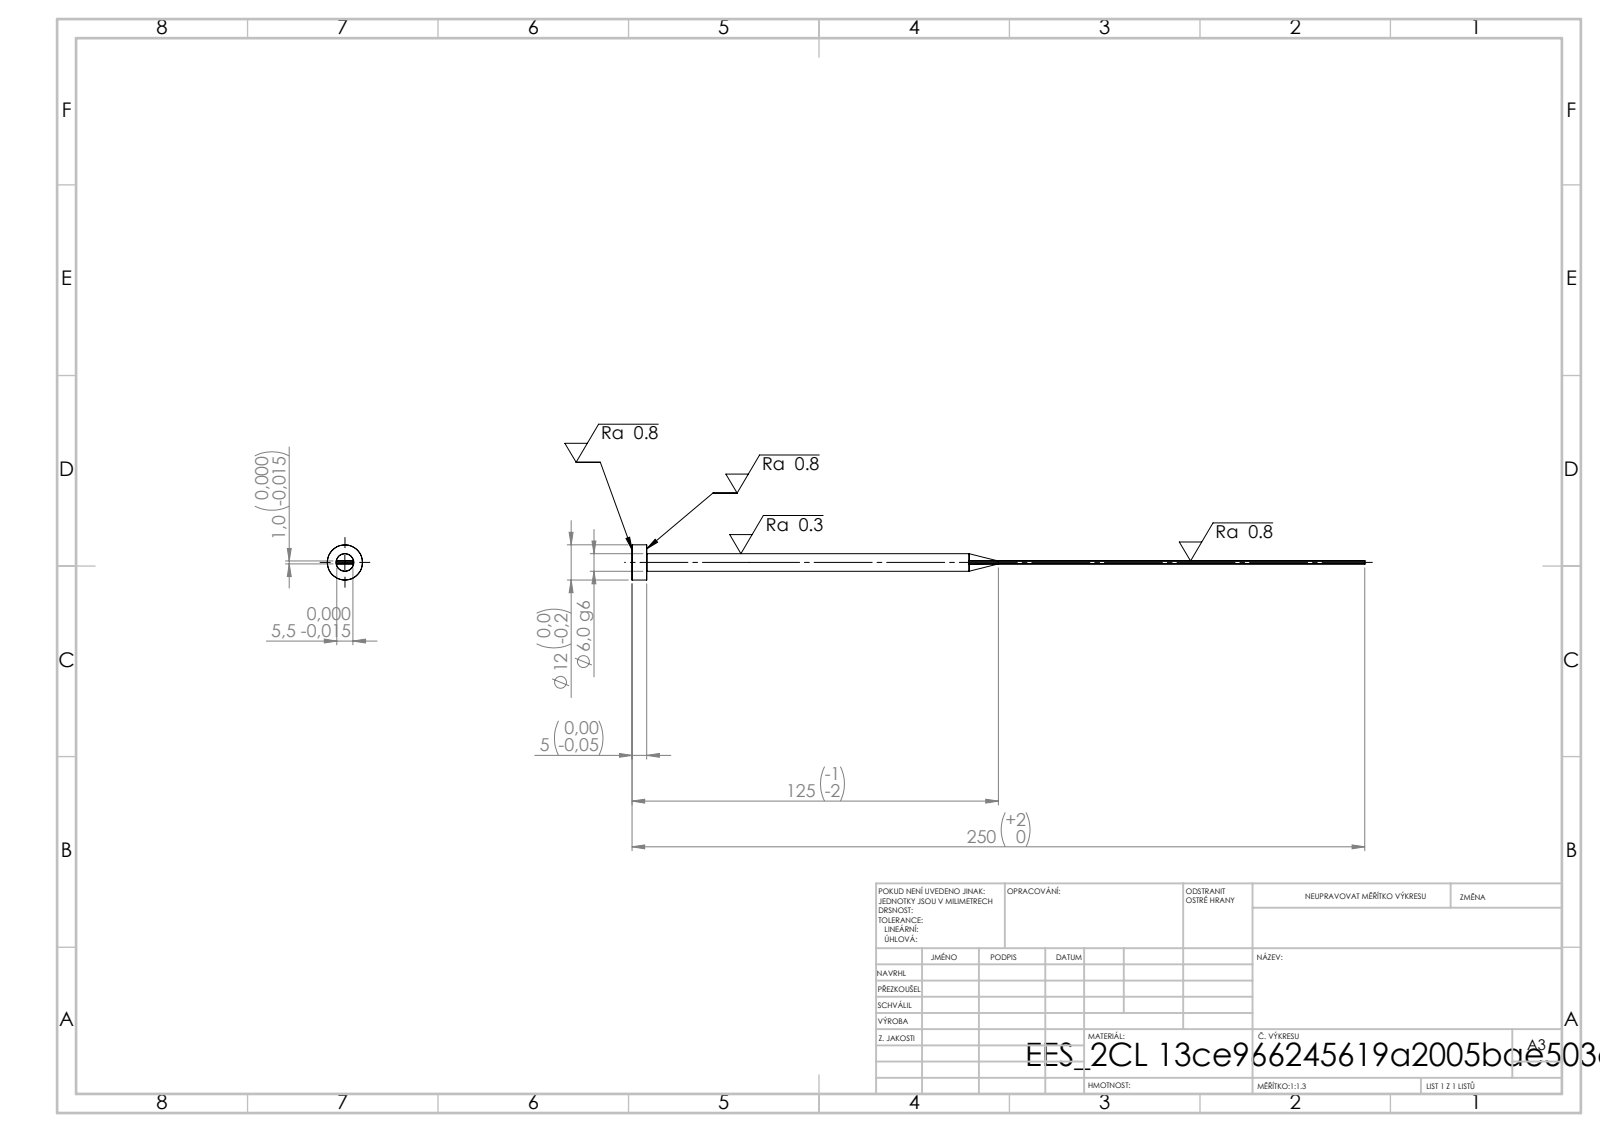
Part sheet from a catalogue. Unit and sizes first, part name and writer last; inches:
Units: inches
Overall size (bounding box): 9.843 × 0.472 × 0.472
Round bosses / shafts (diameter × count): ⌀0.472 ×1, ⌀0.236 ×1
Main face-to-face distances: 0.039, 0.217, 0.197, 9.843, 9.646
Volume: 0.276 in³ · Surface area: 6.578 in²
Bodies: 1 solid, 15 faces (7 planar, 4 cylindrical, 4 other)
STEP written by: SolidWorks 2019 (CONFIG_CONTROL_DESIGN)
